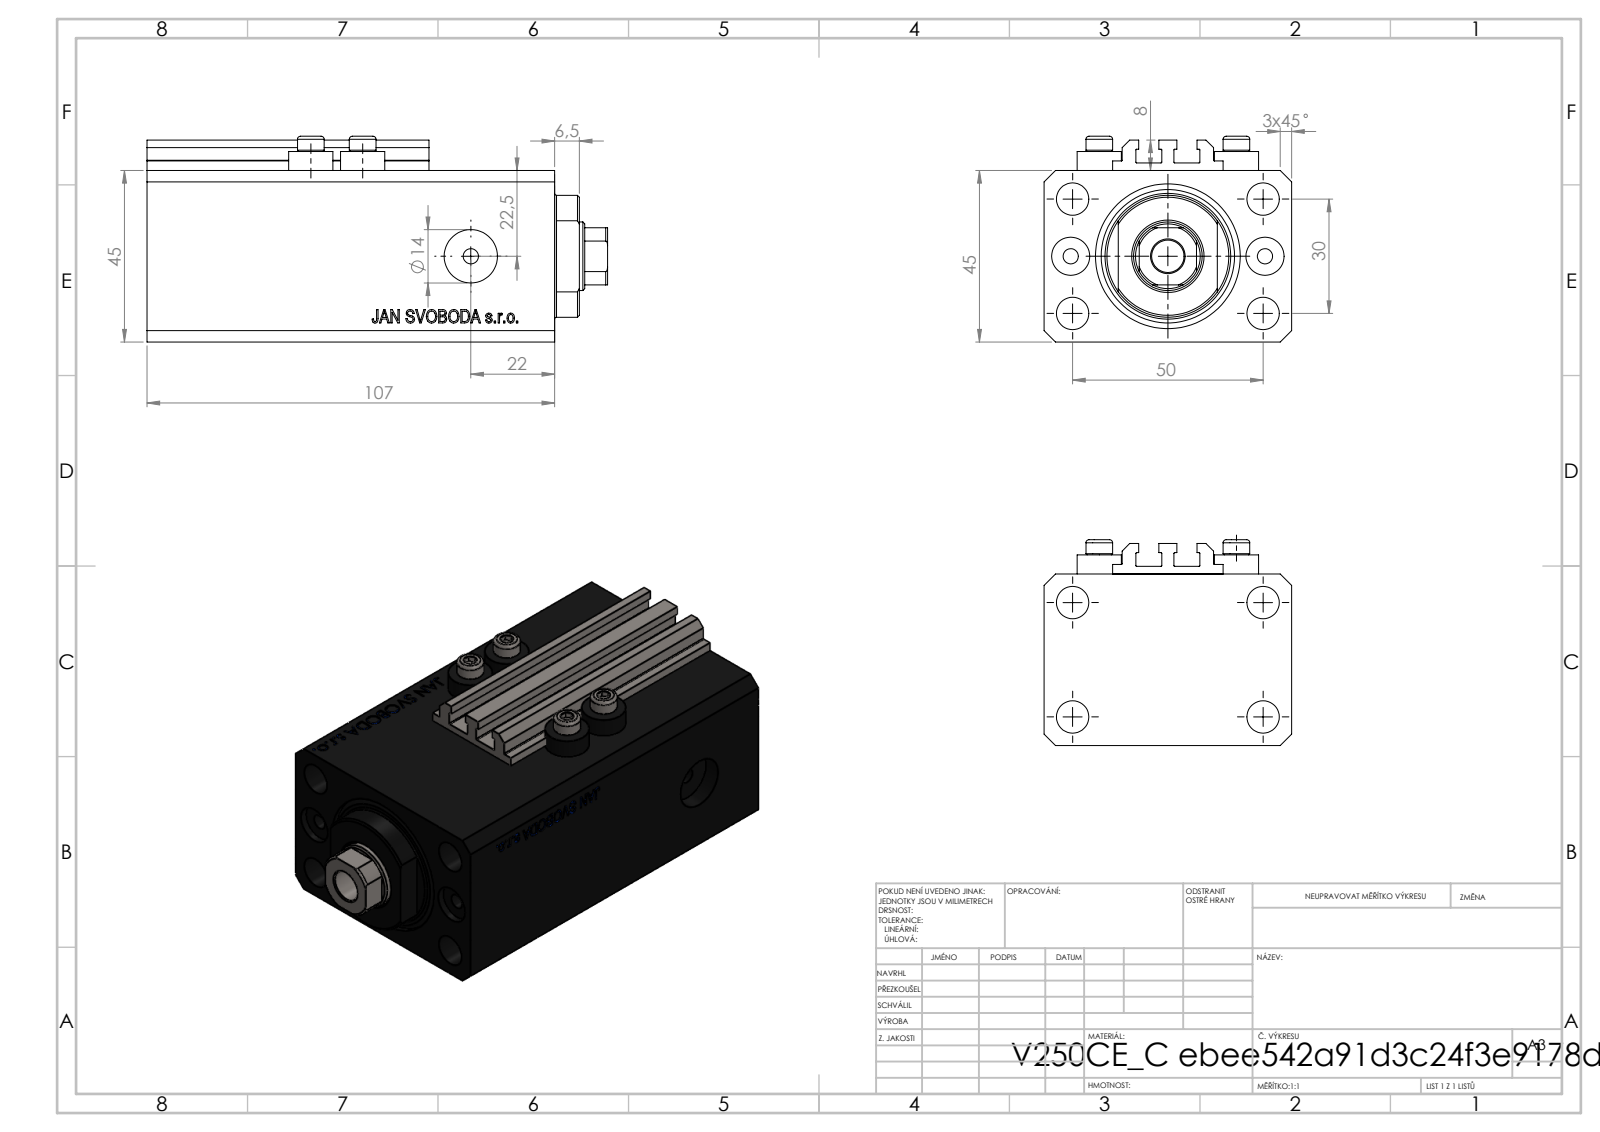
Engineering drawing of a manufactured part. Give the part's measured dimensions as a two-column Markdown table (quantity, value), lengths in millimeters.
| quantity | value |
| --- | --- |
| part name | V250CE_C_Body; V250CE_VC_C; ALLEN BOLT V250CE; V250CE_C_VCP |
| STEP written by | SolidWorks 2019 (CONFIG_CONTROL_DESIGN) |
| units | millimeters |
| bodies | 8 solids, 1033 faces (503 planar, 86 cylindrical, 444 other) |
| overall size | 120.9 × 65 × 54 |
| volume | 288 982 mm³ |
| surface area | 76 094 mm² |
| round holes (diameter × count) | 4 × 8, 8.5 × 5, 10 × 2, 14 × 2, 18 × 1, 25 × 1, 38 × 1 |
| round bosses / shafts (diameter × count) | 11.6 × 4, 7 × 4 |
| partial cylindrical surfaces (radius × count) | 0.2 × 10, 8.5 × 1, 16 × 1 |
| main face-to-face distances | 45, 65, 81.9, 107, 25.1, 47, 2.5, 10, 2, 6.9 |
| hole center spacings | 15.01, 29.15, 52.68, 13.6, 25.5, 30, 36, 38.48 |
